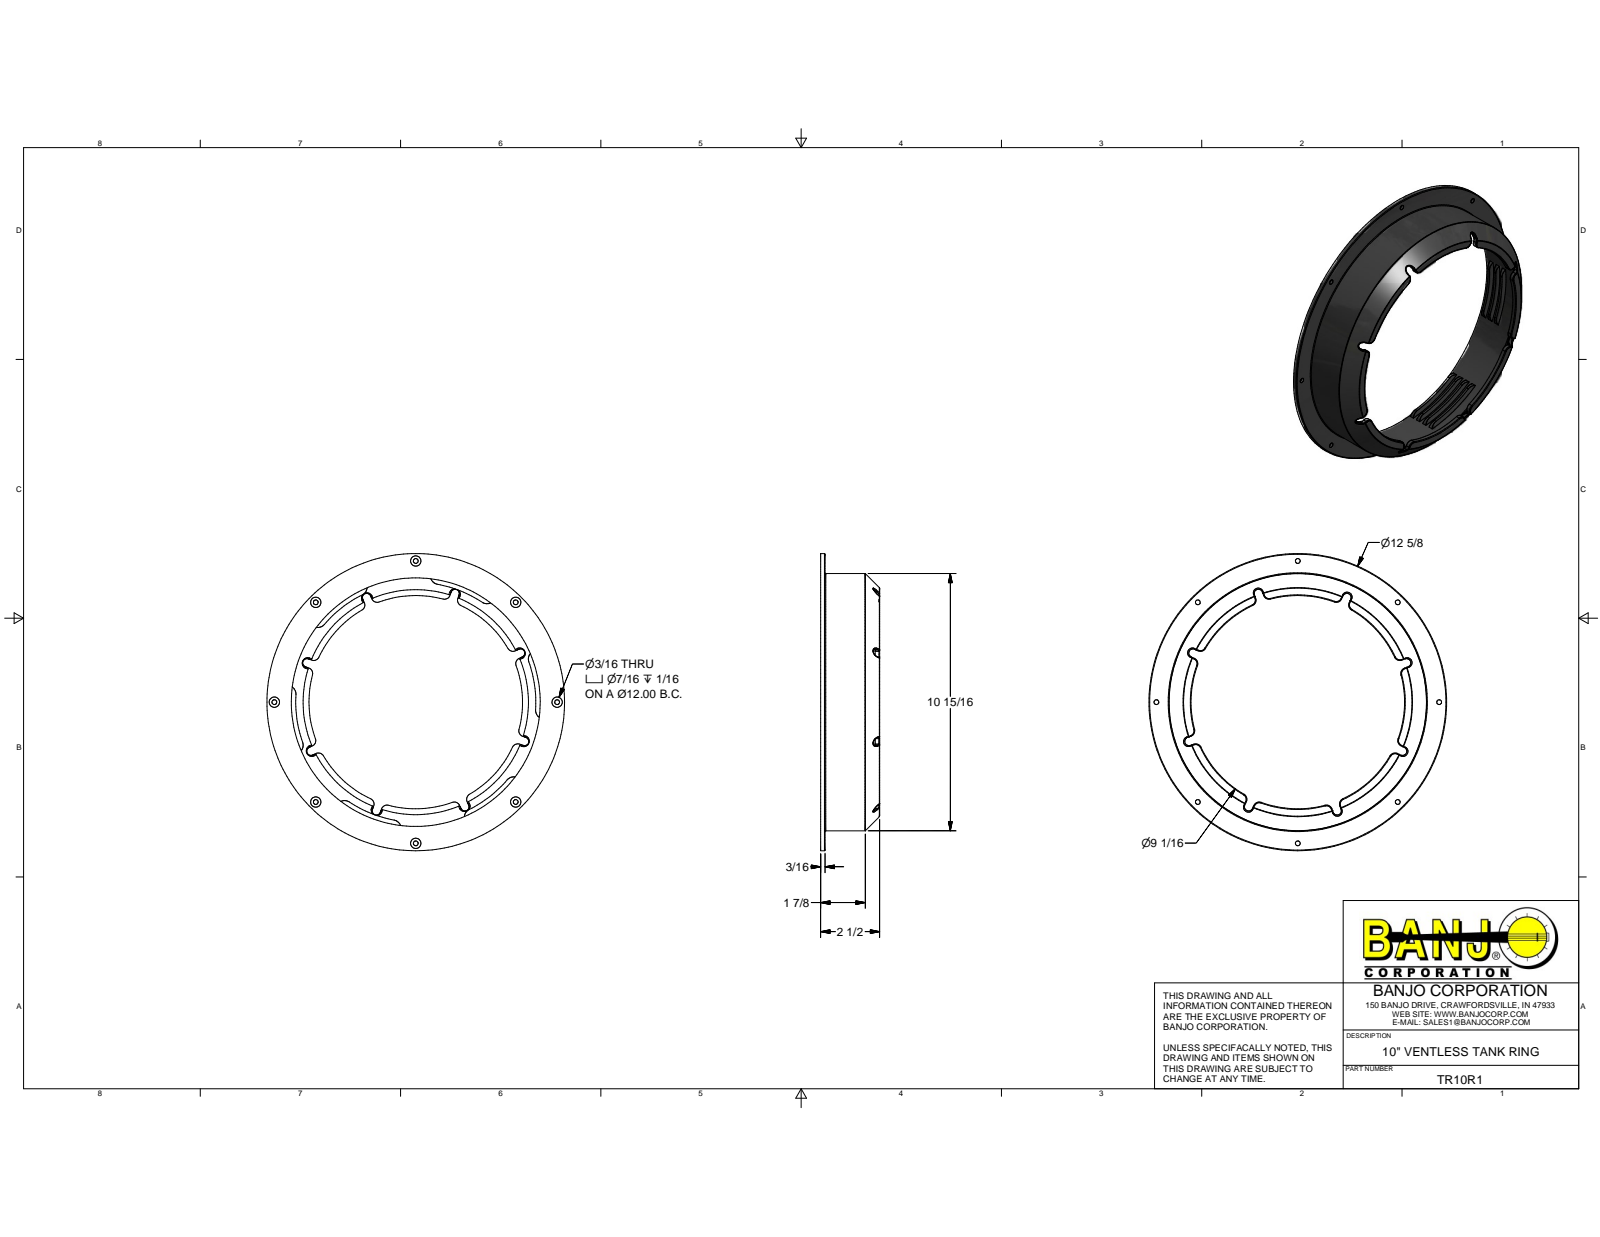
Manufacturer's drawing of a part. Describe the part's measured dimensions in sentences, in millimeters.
The part is named "TR10R1". Its 3-D file was written by "Autodesk Inventor 2014 (AUTOMOTIVE_DESIGN)". It is 1 solid with 310 faces: 42 planar, 127 cylindrical and 141 other. Overall it measures 320.8 by 320.8 by 63.52 millimeters. Its volume is 407 251 cubic millimeters and its surface area 180 618 square millimeters. Round holes: 8 of diameter 5.16, 8 of diameter 11.13, 1 of diameter 268.27. Round bosses or shafts: 1 of diameter 320.8, 1 of diameter 277.83. Partial cylindrical surfaces (rounded edges, fillets, slot ends): 16 of radius 0.76, 16 of radius 6.35, 12 of radius 9.53, 8 of radius 4.52, 1 of radius 115.09, 1 of radius 129.39. The main face-to-face distances are 4.76, 63.53, 58.77, 58.76, 54, 4.77, 1.78, 2.98, 56.98, 61.75. The hole center spacings are 116.64, 152.4, 281.59, 215.52, 215.53, 304.79, 304.8.
